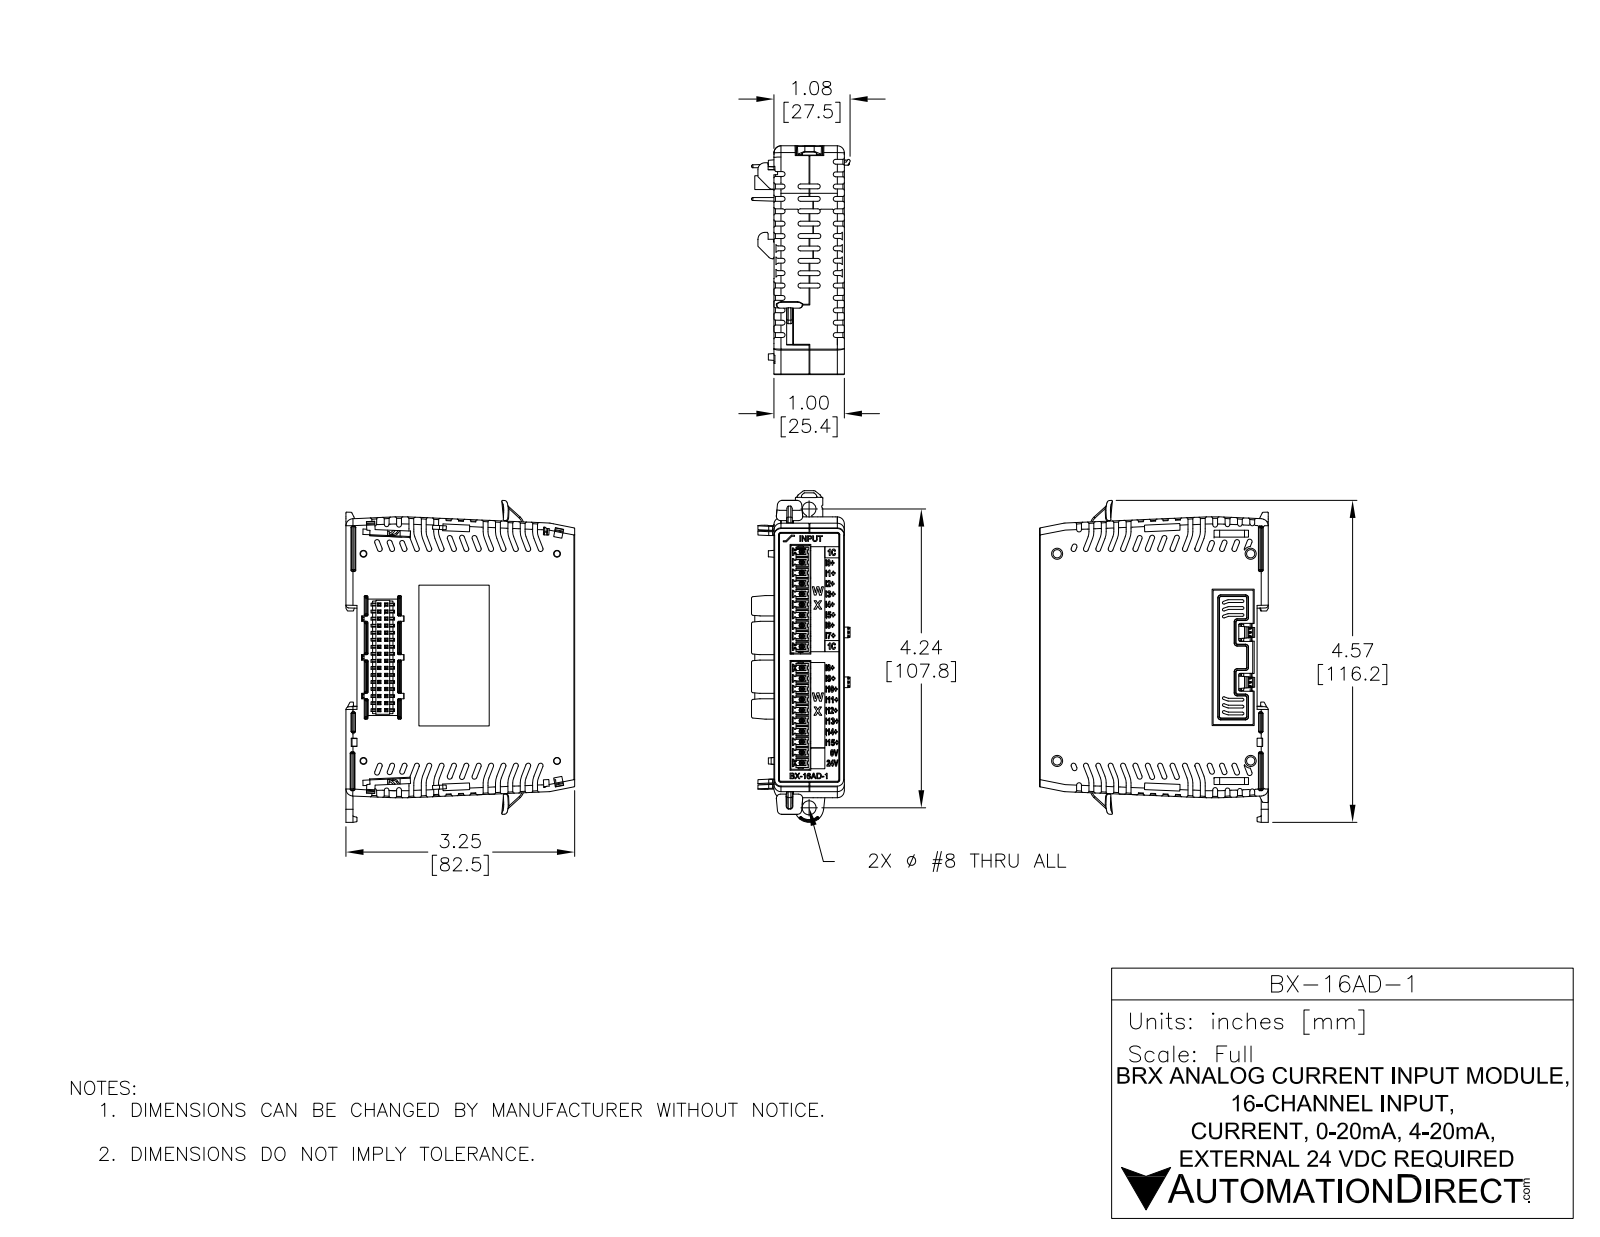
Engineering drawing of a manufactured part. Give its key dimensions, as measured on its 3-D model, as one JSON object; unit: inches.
{"part_name": "BX-16AD-1", "step_written_by": "SolidWorks 2017 (AUTOMOTIVE_DESIGN)", "units": "inches", "bodies": {"solids": 10, "faces": 4874, "planar": 3509, "cylindrical": 627, "other": 738}, "overall_size": [4.586, 3.25, 1.401], "volume_in3": 9.457, "surface_area_in2": 89.26, "round_holes": [[0.016, 8], [0.016, 2], [0.118, 2], [0.118, 2], [0.199, 1]], "round_bosses_or_shafts": [[0.111, 2], [0.059, 2], [0.071, 1]], "partial_cylinders_radius": [[0.02, 109], [0.008, 103], [0.005, 48], [0.062, 20], [0.012, 16], [0.014, 16], [0.01, 14], [0.008, 12]], "face_to_face_distances": [1, 0.835, 0.165, 3.053, 0.209, 0.627, 0.791, 3.063, 2.053, 1.01], "hole_center_spacings": [0.15, 0.3, 0.45, 0.6, 0.75, 1.651, 0.9, 1.501]}
